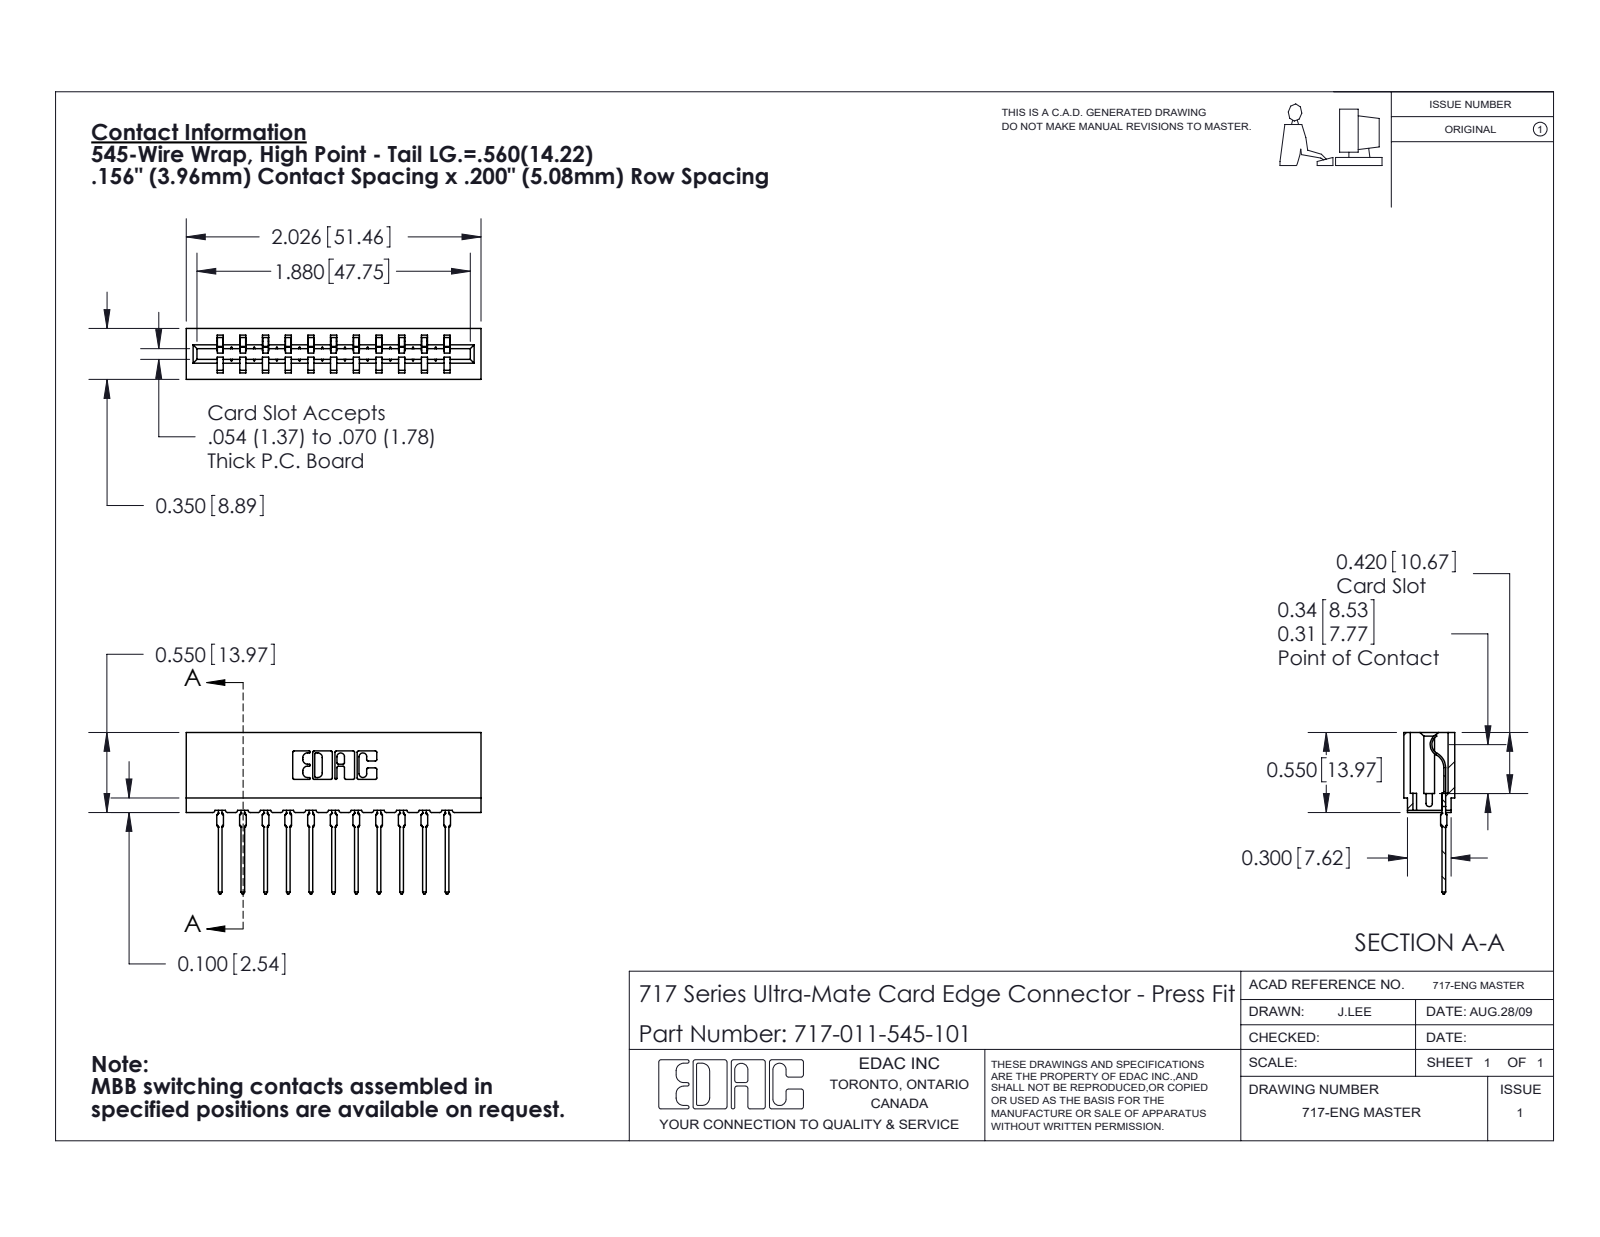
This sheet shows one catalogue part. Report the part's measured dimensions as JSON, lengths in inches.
{"part_name": "717-011-545-101; 717 Part_Insulator Option - 06; 745-292-001_545", "step_written_by": "SolidWorks 2020 (CONFIG_CONTROL_DESIGN)", "units": "inches", "bodies": {"solids": 12, "faces": 1337, "planar": 802, "cylindrical": 249, "other": 286}, "overall_size": [2.026, 1.109, 0.35], "volume_in3": 0.276, "surface_area_in2": 9.58, "partial_cylinders_radius": [[0.01, 22], [0.015, 22], [0.021, 22], [0.007, 6], [0.031, 6], [0.005, 4], [0.011, 4], [0.026, 3]], "face_to_face_distances": [0.212, 0.156, 0.138, 0.468, 0.624, 0.35, 0.312, 0.198, 0.312, 0.042]}
